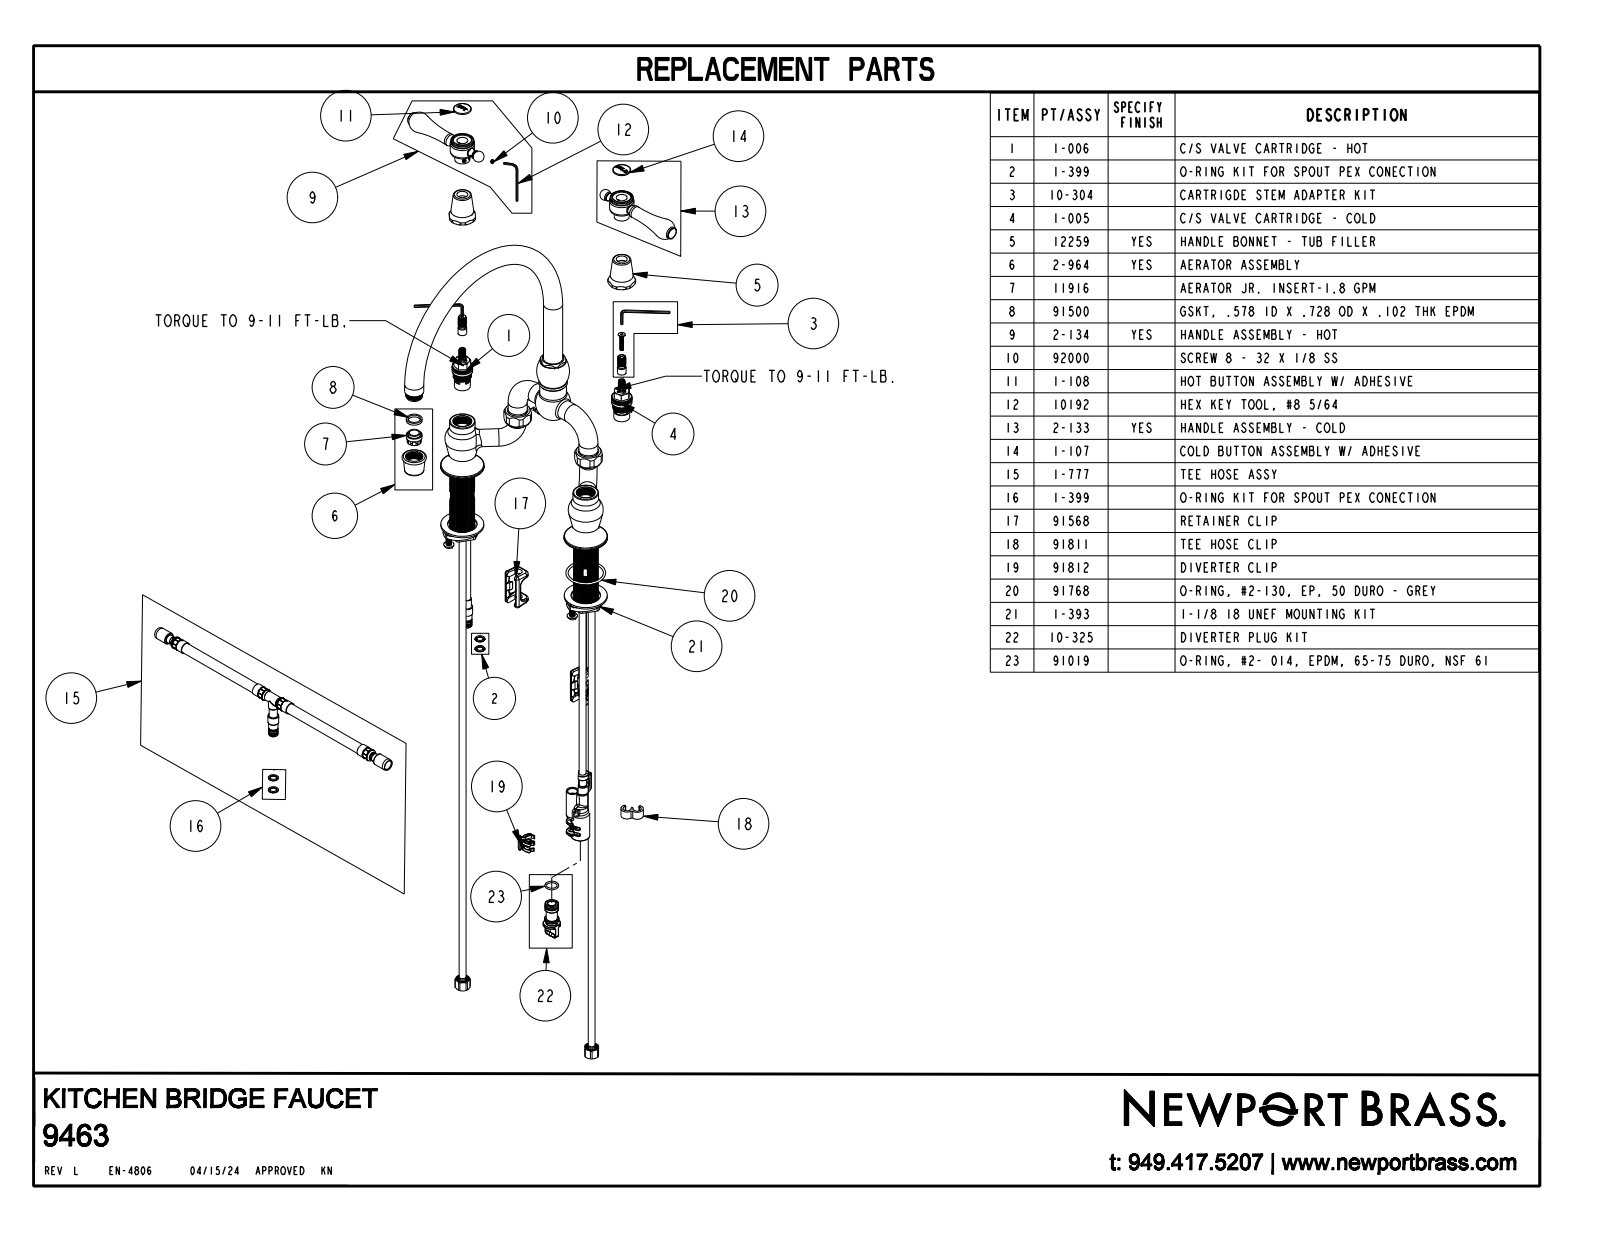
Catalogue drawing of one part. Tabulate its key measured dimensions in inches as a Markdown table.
| quantity | value |
| --- | --- |
| part name | 9463 |
| STEP written by | CREO PARAMETRIC BY PTC INC, 2018400 (AUTOMOTIVE_DESIGN) |
| units | inches |
| bodies | 3 solids, 313 faces (59 planar, 74 cylindrical, 180 other) |
| overall size | 15.134 × 14.745 × 10.367 |
| volume | 34.51 in³ |
| surface area | 156.8 in² |
| round bosses / shafts (diameter × count) | 0.874 × 3, 1.917 × 2, 1.115 × 2, 1.102 × 2, 1.055 × 2, 0.875 × 2, 0.8 × 2, 0.687 × 2 |
| partial cylindrical surfaces (radius × count) | 0.637 × 2, 0.196 × 1, 0.6 × 1 |
| main face-to-face distances | 3.096, 1.188, 2.362, 0.734, 2.296, 3.136, 0.774, 0.04, 2.516, 0.154 |
